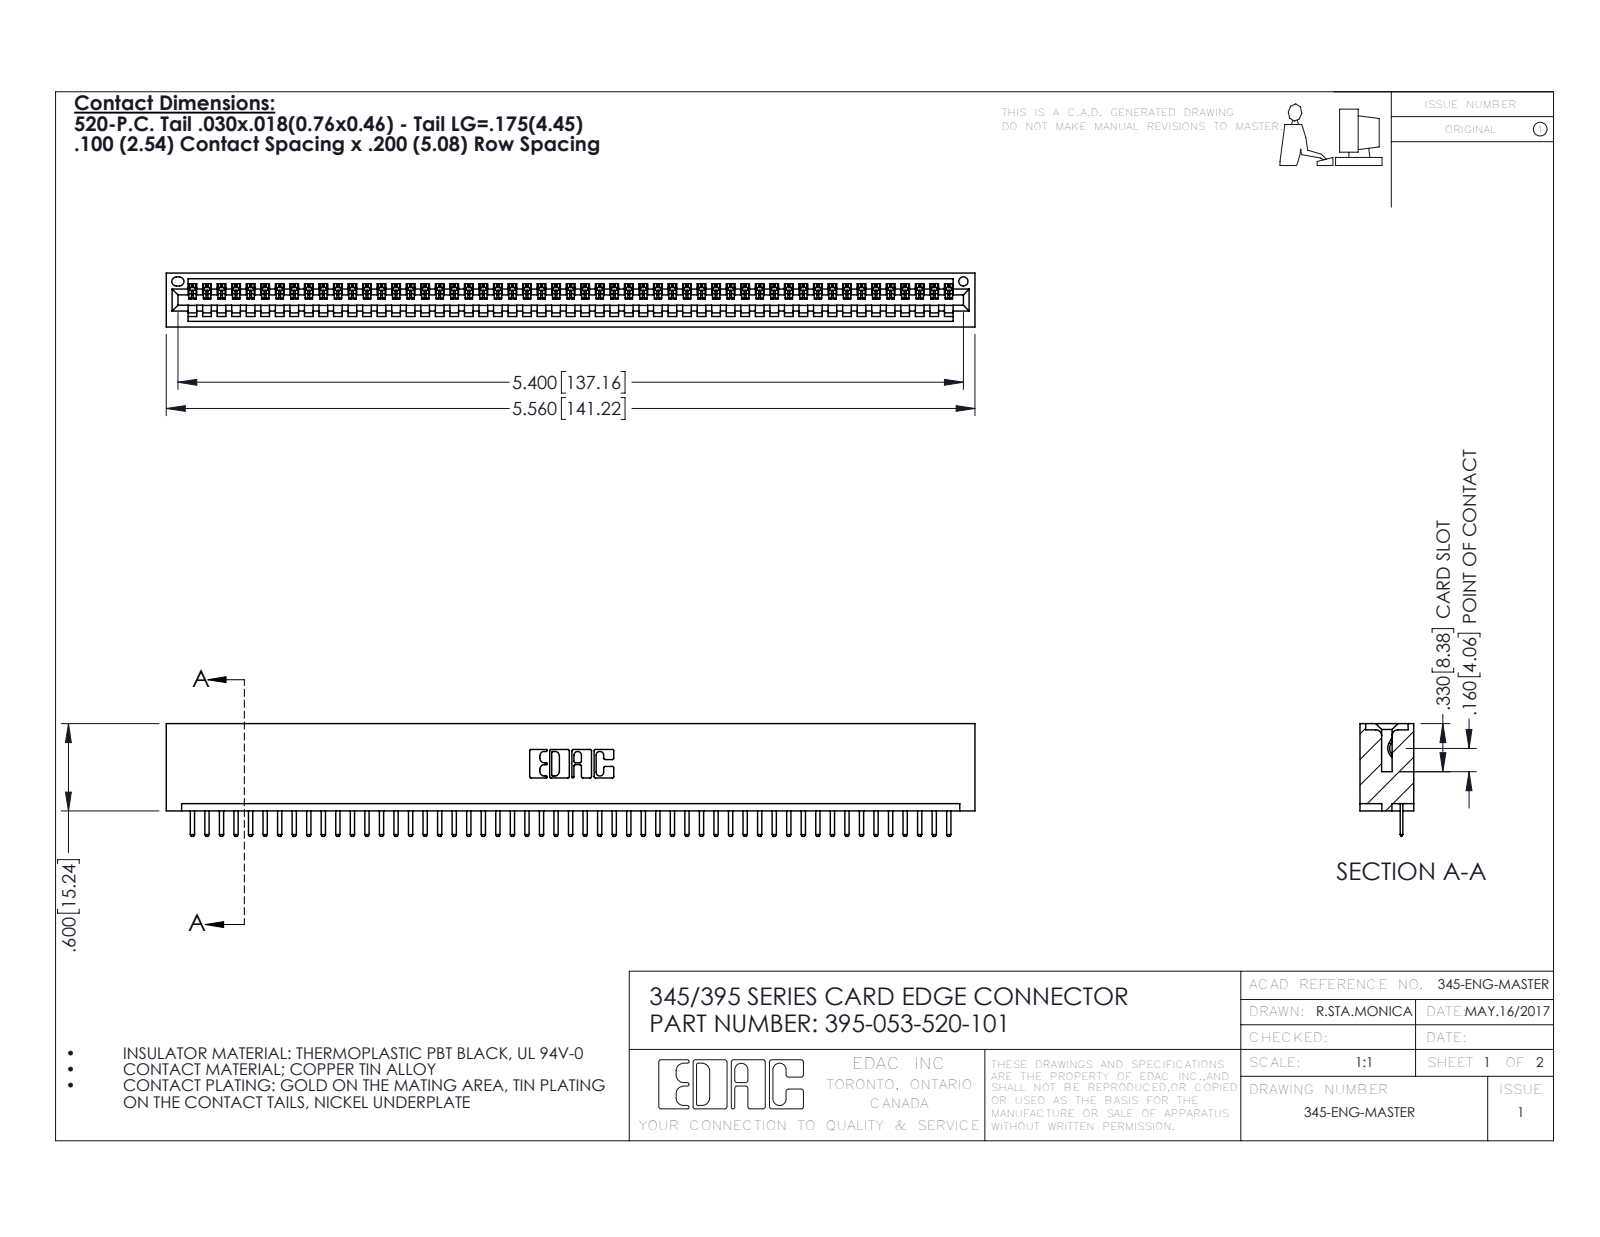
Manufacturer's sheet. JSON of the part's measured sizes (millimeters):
{"part_name": "395-053-520-101; 345 Part_No Mounting Lugs; 345-292-001_345-293-120", "step_written_by": "SolidWorks 2016 (CONFIG_CONTROL_DESIGN)", "units": "millimeters", "bodies": {"solids": 54, "faces": 3404, "planar": 2302, "cylindrical": 1102, "other": 0}, "overall_size": [141.2, 19.7, 9.4], "volume_mm3": 13900, "surface_area_mm2": 18360, "round_holes": [[1.6, 1]], "partial_cylinders_radius": [[0.3, 108], [0.2, 106], [0.3, 22], [0.2, 6], [0.8, 6], [0.7, 3], [0.8, 2], [1, 2]], "face_to_face_distances": [7.6, 1.8, 9.4, 5.1, 2.5, 6.9, 0.6, 5.7, 1.8, 3.8]}
